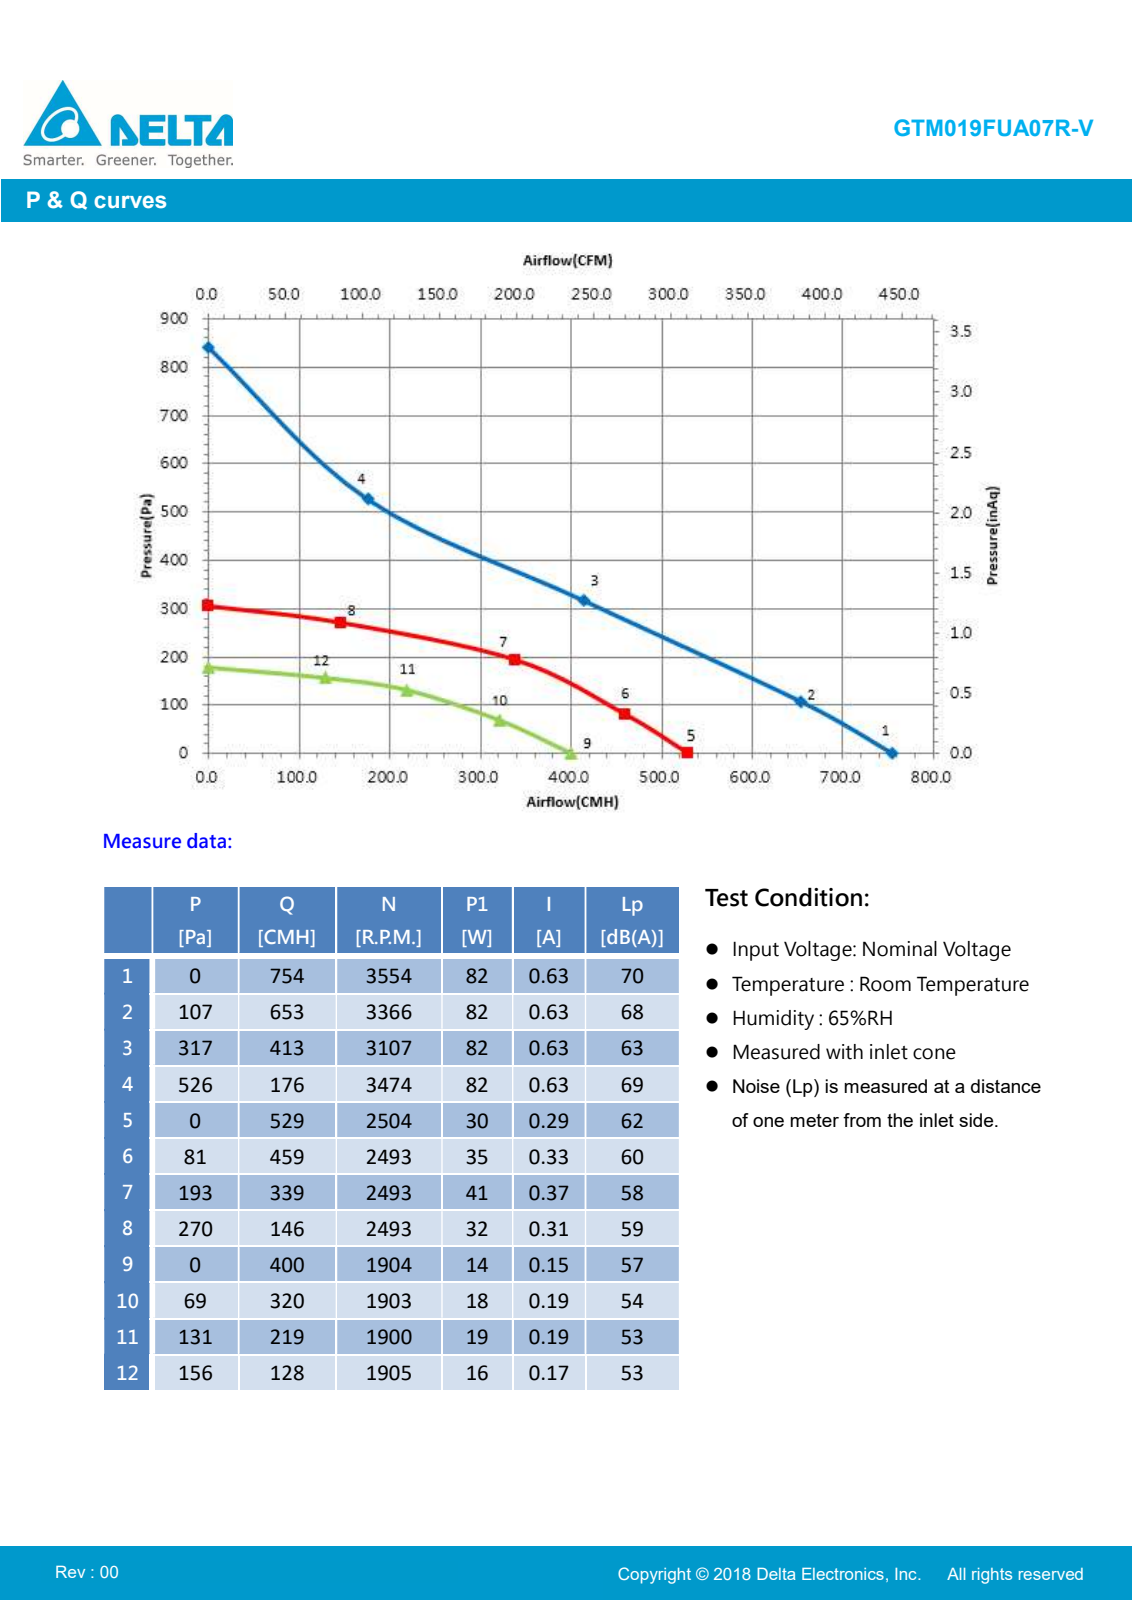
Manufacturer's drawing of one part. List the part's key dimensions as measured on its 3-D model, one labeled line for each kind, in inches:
Part name (STEP PRODUCT): 41021295000_4; 41021296000_3; 3323299500_2; TORX_M4_L6_1 (+8 more)
STEP written by: CREO PARAMETRIC BY PTC INC, 2015080 (CONFIG_CONTROL_DESIGN)
Units: inches
Bodies: 21 solids, 4647 faces (1826 planar, 1343 cylindrical, 1478 other)
Overall size (bounding box): 8.858 × 8.858 × 3.463
Volume: 42.84 in³ · Surface area: 762.9 in²
Round holes (diameter × count): ⌀0.236 ×16, ⌀0.126 ×9, ⌀0.197 ×7, ⌀0.13 ×6, ⌀0.169 ×4, ⌀0.177 ×4, ⌀0.181 ×4, ⌀0.185 ×4, ⌀0.335 ×4, ⌀0.098 ×3, ⌀0.118 ×3, ⌀0.165 ×3
Round bosses / shafts (diameter × count): ⌀0.102 ×8, ⌀0.157 ×7, ⌀0.315 ×5, ⌀0.394 ×4, ⌀0.335 ×3, ⌀0.236 ×3, ⌀0.209 ×3, ⌀0.197 ×3
Partial cylindrical surfaces — rounded edges, fillets, slot ends (radius × count): R0.02 ×48, R0.039 ×39, R0.008 ×28, R0.016 ×24, R0.059 ×24, R0.079 ×21, R0.787 ×16, R0.197 ×14
Main face-to-face distances: 0.098, 0.055, 0.043, 3.346, 3.248, 3.291, 2.484, 0.492, 0.252, 2.996
Hole centre spacings: 5.283, 0.335, 0.795, 1.425, 2.38, 2.44, 2.958, 3.11
